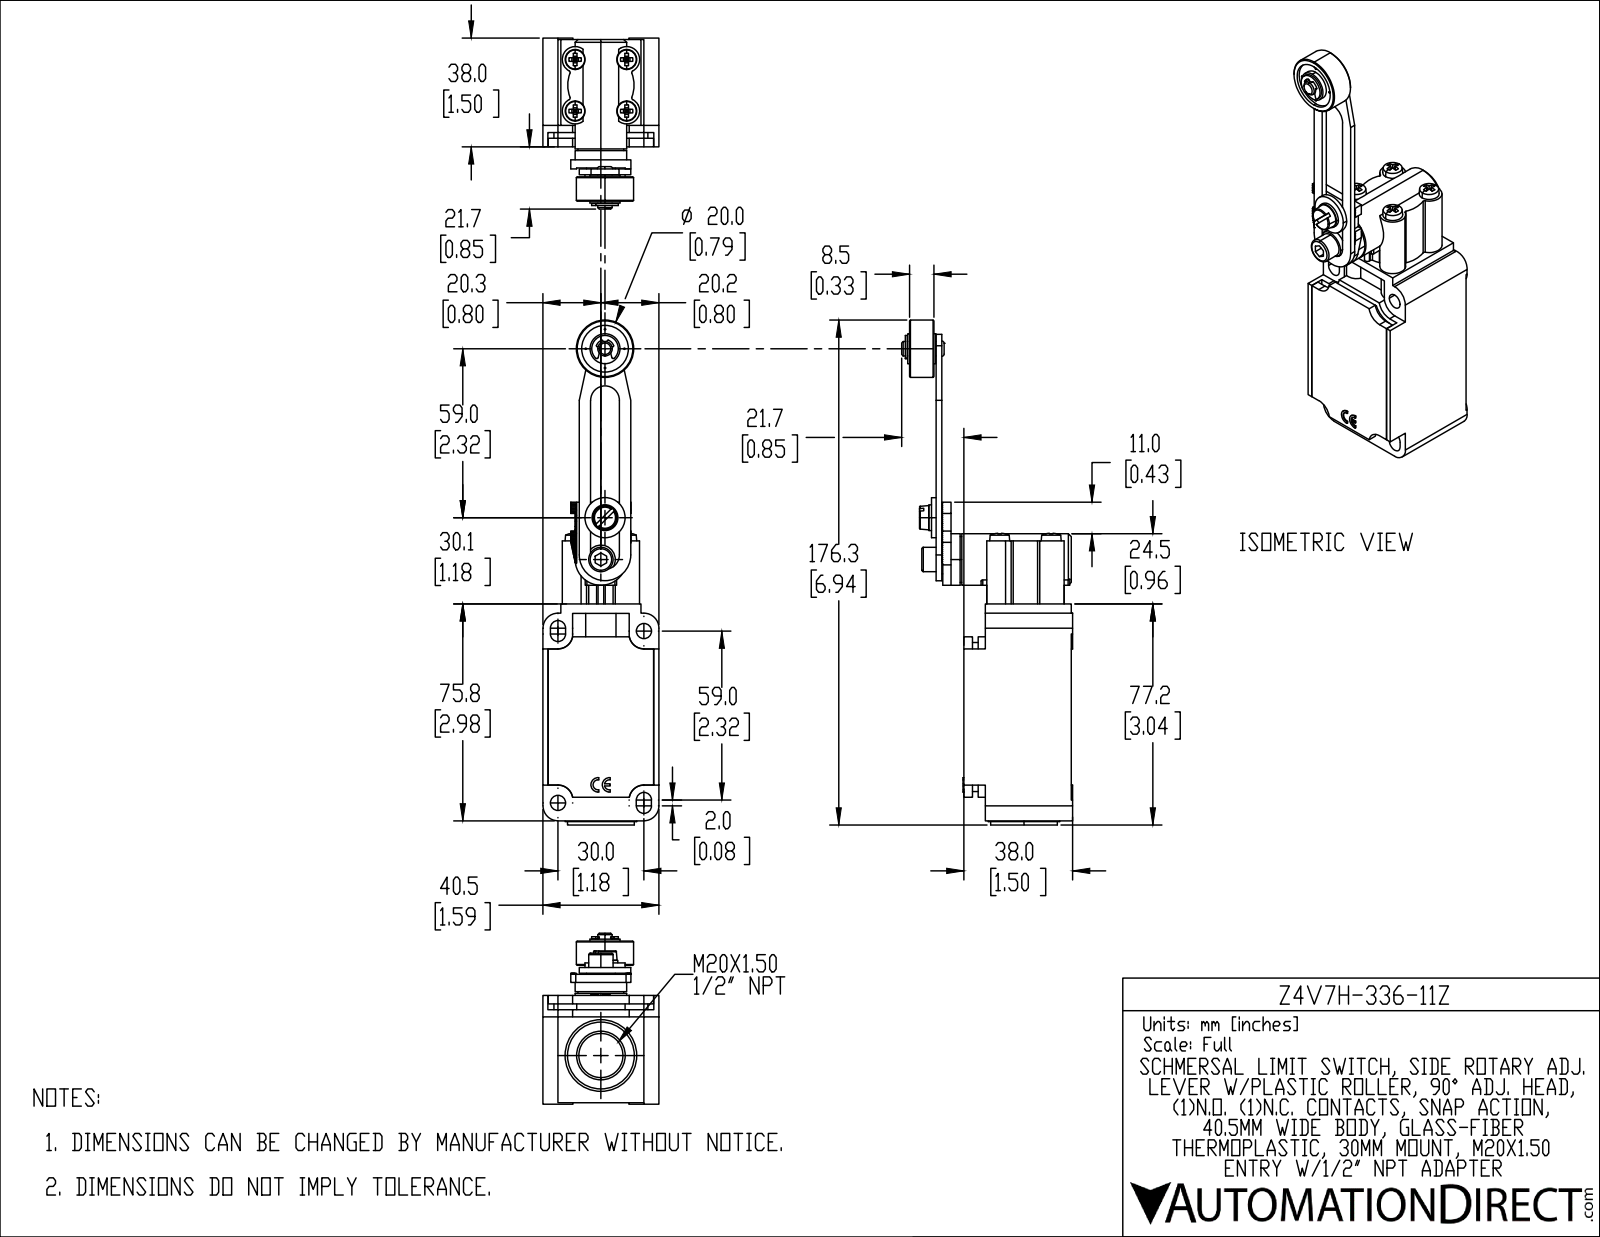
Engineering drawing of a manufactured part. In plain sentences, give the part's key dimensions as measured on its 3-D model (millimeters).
The part is named "Z4V7H-336-11Z". Its 3-D file was written by "SolidWorks 2019 (AUTOMOTIVE_DESIGN)". It is 1 solid with 613 faces: 432 planar, 145 cylindrical and 36 other. Overall it measures 176.3 by 59.7 by 40.5 millimeters. Its volume is 125 600 cubic millimeters and its surface area 27 480 square millimeters. Round holes: 4 of diameter 0.5, 2 of diameter 5.3, 1 of diameter 16.3, 1 of diameter 16.5, 1 of diameter 17. Round bosses or shafts: 1 of diameter 25, 1 of diameter 23.3, 1 of diameter 20, 1 of diameter 18, 1 of diameter 16, 1 of diameter 14, 1 of diameter 10.5, 1 of diameter 10. Partial cylindrical surfaces (rounded edges, fillets, slot ends): 16 of radius 0.6, 8 of radius 5.2, 8 of radius 5.3, 4 of radius 0.3, 4 of radius 2.6, 4 of radius 4.5, 4 of radius 7.2, 2 of radius 0.5. The main face-to-face distances are 40.5, 37.5, 2, 7.5, 9.7, 47.2, 4.5, 30, 7.7, 45.2. The hole center spacings are 6.8, 9.6, 13.5, 29.2, 66.9, 67.1, 73.6, 73.8.
